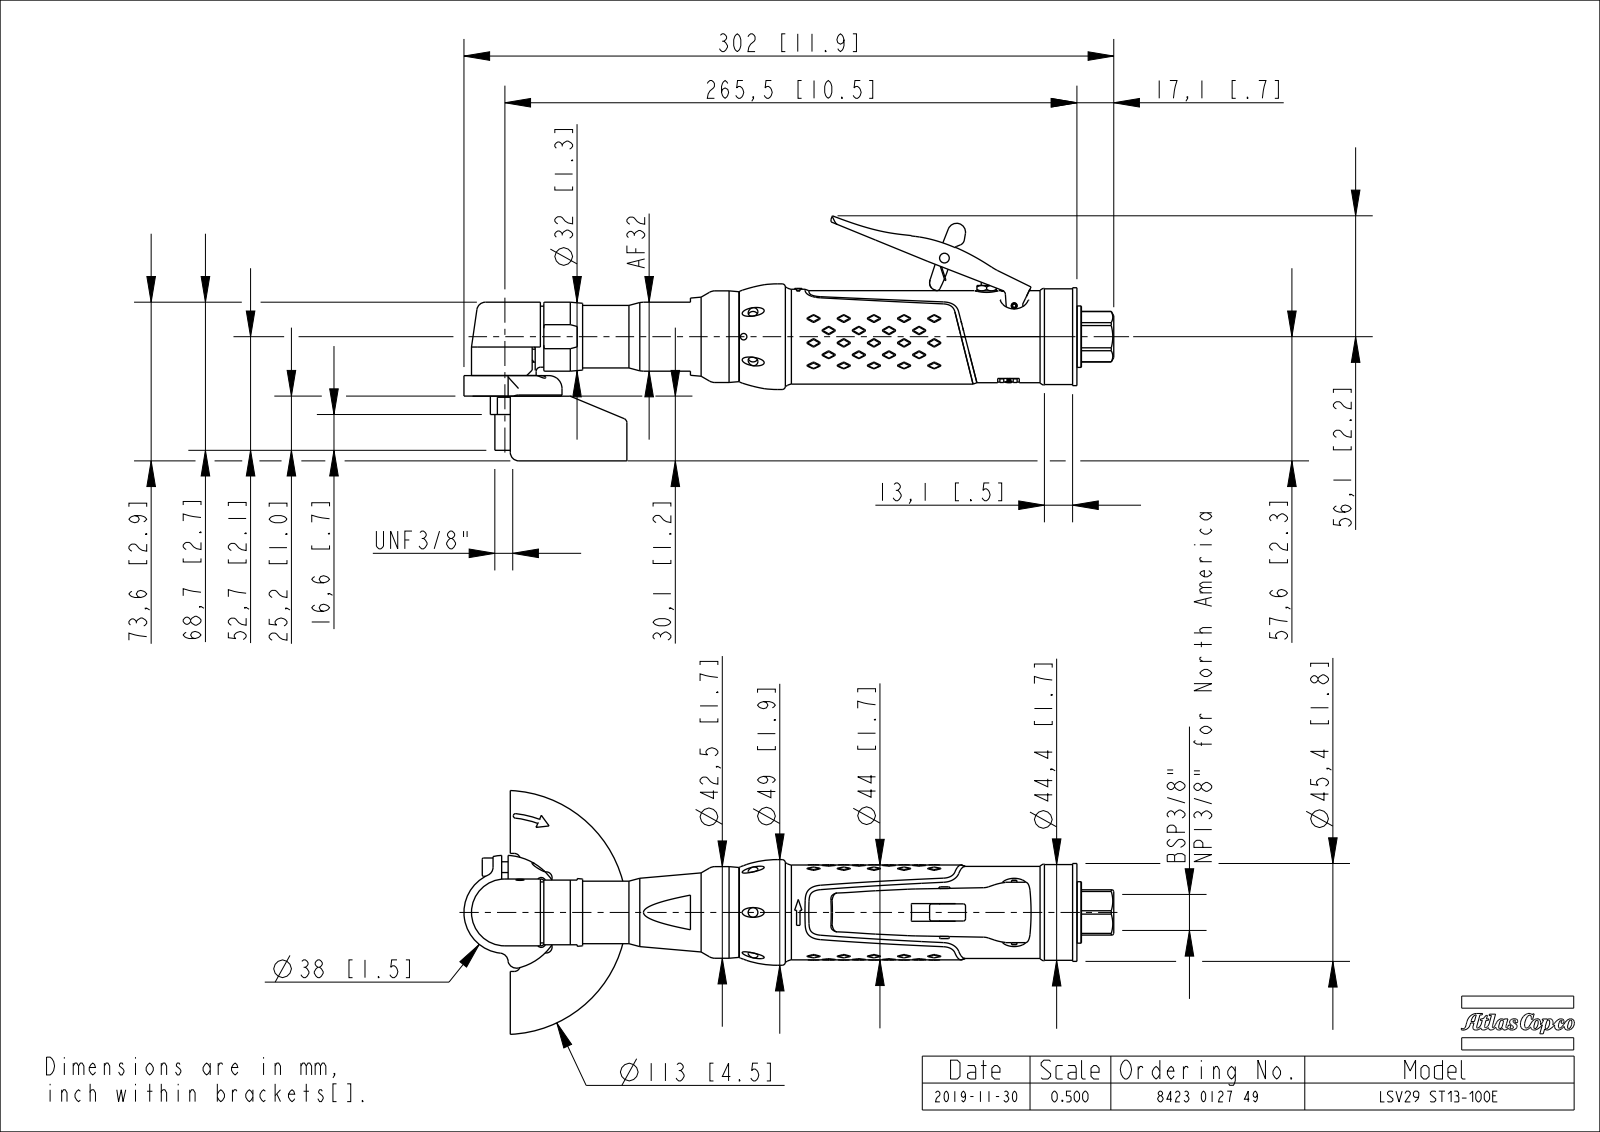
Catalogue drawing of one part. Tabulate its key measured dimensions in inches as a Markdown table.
| quantity | value |
| --- | --- |
| part name | EXT_COMP_SW0040 |
| STEP written by | CREO PARAMETRIC BY PTC INC, 2018100 (AP242_MANAGED_MODEL_BASED_3D_ENGINEERING_MIM_LF) |
| units | inches |
| bodies | 3 solids, 1533 faces (503 planar, 290 cylindrical, 740 other) |
| overall size | 11.872 × 4.475 × 4.452 |
| volume | 23.47 in³ |
| surface area | 123.2 in² |
| round holes (diameter × count) | 0.163 × 4, 0.177 × 3, 0.217 × 3, 0.059 × 1, 0.098 × 1, 0.118 × 1, 0.15 × 1, 0.157 × 1, 0.205 × 1, 0.535 × 1, 0.598 × 1, 1.035 × 1 |
| round bosses / shafts (diameter × count) | 0.197 × 5, 0.472 × 3, 0.433 × 3, 0.02 × 3, 1.929 × 1, 1.787 × 1, 1.748 × 1, 1.694 × 1 |
| partial cylindrical surfaces (radius × count) | 0.039 × 16, 0.157 × 9, 0.108 × 7, 0.748 × 5, 0.03 × 3, 0.051 × 3, 0.134 × 2, 0.63 × 2 |
| main face-to-face distances | 0.039, 0.142, 0.102, 0.063, 1.717, 1.715, 0.059, 0.065, 1.78, 0.376 |
| hole center spacings | 0.593, 3.91, 1.113, 1.22, 1.543, 3.667, 3.939, 4.088 |
